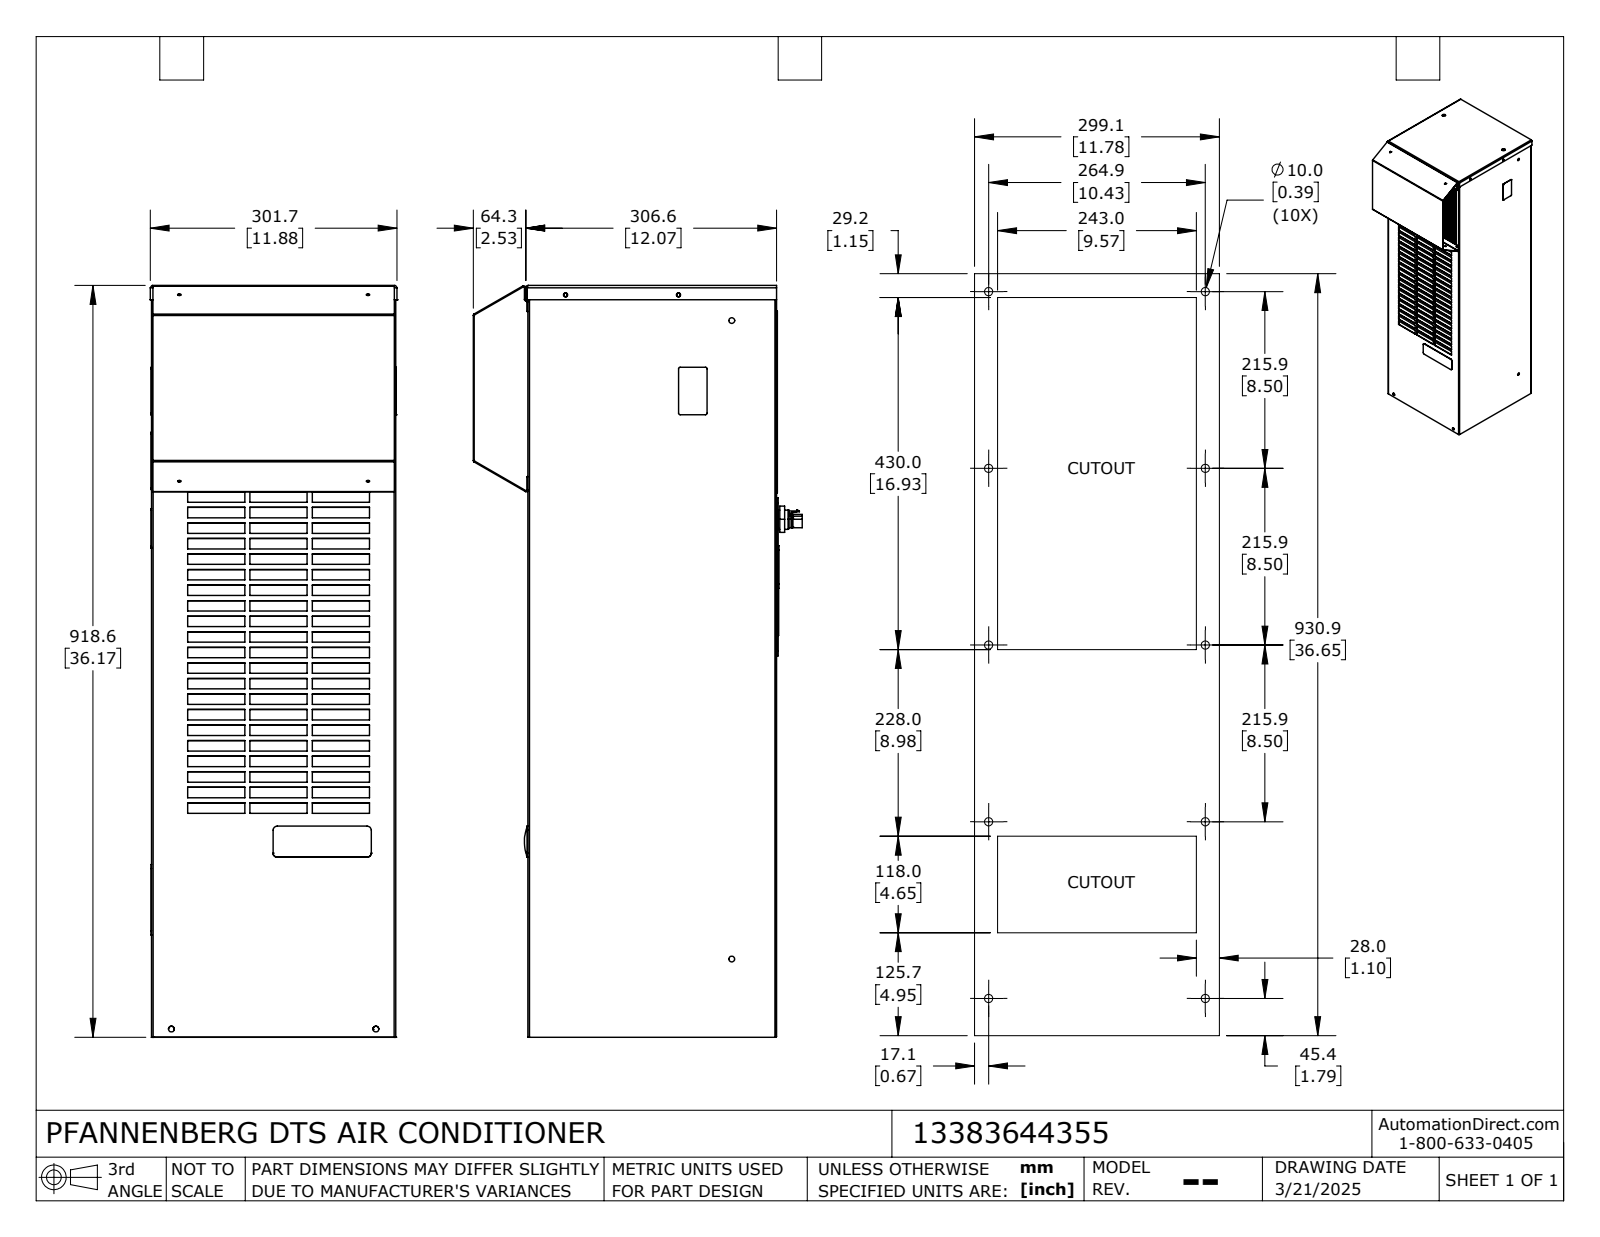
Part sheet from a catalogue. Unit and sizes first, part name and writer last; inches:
Units: inches
Overall size (bounding box): 36.166 × 15.829 × 11.878
Round holes (diameter × count): ⌀0.165 ×35, ⌀0.189 ×10, ⌀0.276 ×6, ⌀0.169 ×5, ⌀0.209 ×5, ⌀0.122 ×4, ⌀0.161 ×4, ⌀0.17 ×2, ⌀0.203 ×2, ⌀0.394 ×2, ⌀0.945 ×2, ⌀0.315 ×1
Round bosses / shafts (diameter × count): ⌀0.079 ×4, ⌀0.866 ×2, ⌀1.378 ×1, ⌀0.906 ×1
Partial cylindrical surfaces — rounded edges, fillets, slot ends (radius × count): R0.125 ×112, R0.031 ×19, R0.079 ×12, R0.197 ×12, R0.087 ×10, R0.236 ×10, R0.076 ×8, R0.078 ×4
Main face-to-face distances: 11.811, 11.752, 0.045, 11.843, 0.031, 11.888, 0.076, 0.056, 0.028, 11.839
Hole centre spacings: 0.294, 4.398, 6.602, 0.244, 0.231, 0.254, 0.454, 0.755
Volume: 4 957 in³ · Surface area: 4 044 in²
Bodies: 1 solid, 1788 faces (1242 planar, 493 cylindrical, 53 other)
Part name (STEP PRODUCT): 13383644355_Default
STEP written by: SolidWorks 2024 (CONFIG_CONTROL_DESIGN)
